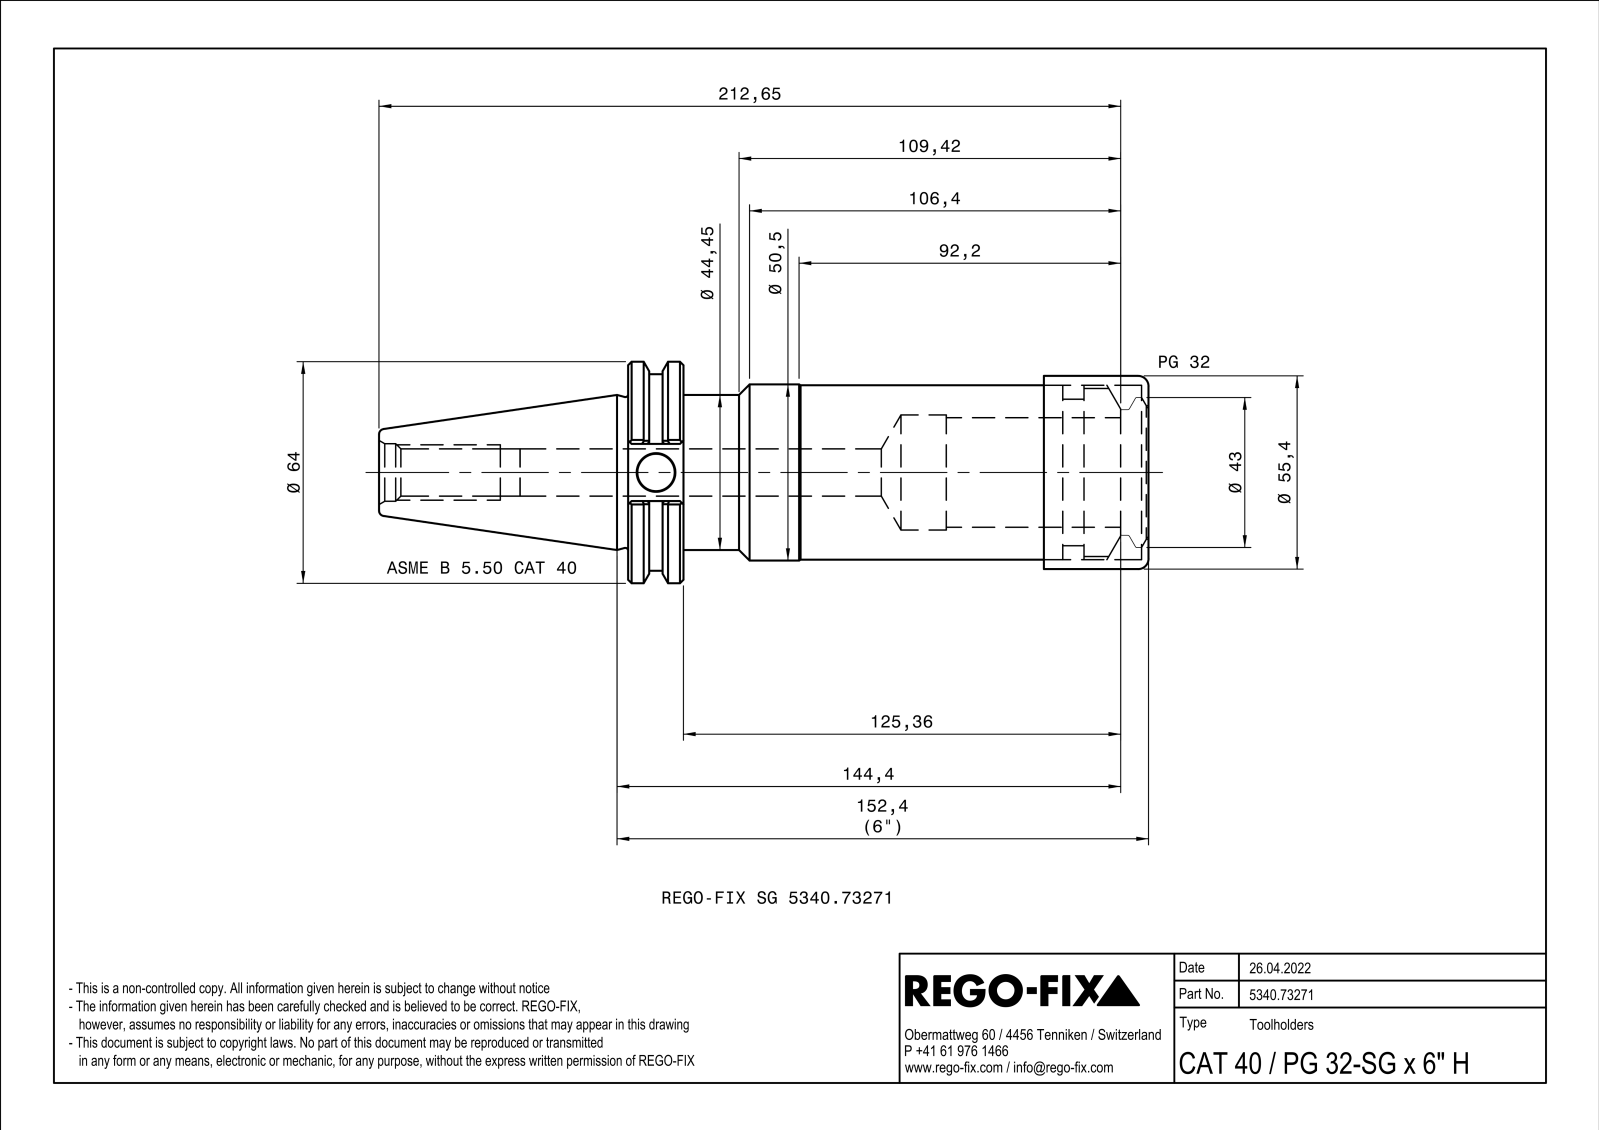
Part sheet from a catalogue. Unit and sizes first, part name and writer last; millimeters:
Units: millimetres
Overall size (bounding box): 220.65 × 63.5 × 60.79
Round holes (diameter × count): ⌀10.7 ×1, ⌀13.53 ×1, ⌀16.5 ×1, ⌀33 ×1, ⌀38.25 ×1, ⌀48.38 ×1, ⌀50.05 ×1, ⌀51 ×1
Round bosses / shafts (diameter × count): ⌀63.5 ×1, ⌀56.36 ×1, ⌀55.4 ×1, ⌀55 ×1, ⌀50.5 ×1, ⌀50 ×1, ⌀44.45 ×1, ⌀42 ×1
Partial cylindrical surfaces — rounded edges, fillets, slot ends (radius × count): R0.5 ×4
Main face-to-face distances: 15.87, 133.36, 149.23, 24.6, 108.76, 124.63, 18.5, 6.1, 114.86, 130.73
Volume: 285 906 mm³ · Surface area: 59 247 mm²
Bodies: 1 solid, 108 faces (36 planar, 24 cylindrical, 48 other)
Part name (STEP PRODUCT): NOCUT
STEP written by: SIEMENS PLM Software Solid Edge ST10 (AUTOMOTIVE_DESIGN)
